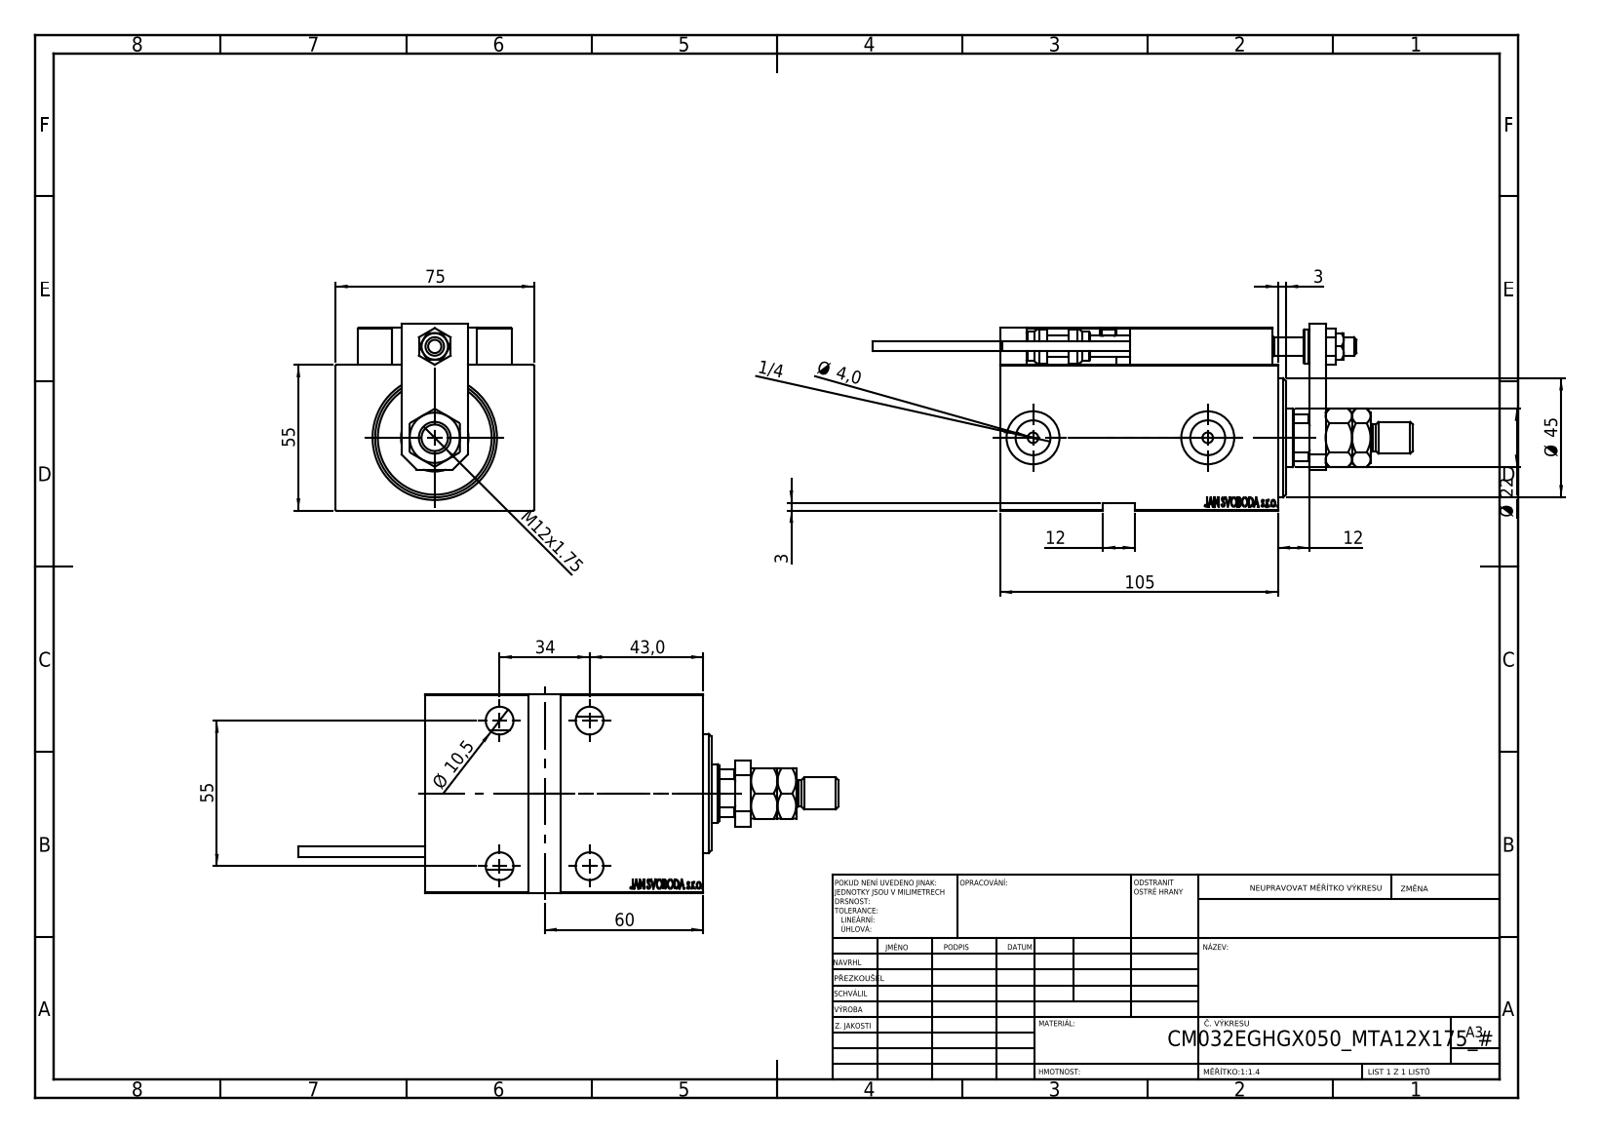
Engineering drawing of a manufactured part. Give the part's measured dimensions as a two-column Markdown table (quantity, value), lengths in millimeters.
| quantity | value |
| --- | --- |
| part name | SWITCH_X_FRONT_BACK; SWITCH X; SWITCH DIM B,W; ALLEN BOLT D5 (+7 more) |
| STEP written by | SolidWorks 2019 (CONFIG_CONTROL_DESIGN) |
| units | millimeters |
| bodies | 25 solids, 1339 faces (584 planar, 184 cylindrical, 571 other) |
| overall size | 204 × 75 × 70.5 |
| volume | 443 266 mm³ |
| surface area | 98 809 mm² |
| round holes (diameter × count) | 4 × 6, 8 × 5, 10.5 × 5, 16.5 × 5, 3.2 × 4, 5 × 2, 13.16 × 2, 20 × 2, 7 × 1, 22 × 1, 25.5 × 1, 32 × 1 |
| round bosses / shafts (diameter × count) | 5 × 2, 3.8 × 2, 34 × 1, 13 × 1, 12 × 1, 11 × 1, 10 × 1 |
| partial cylindrical surfaces (radius × count) | 0.3 × 30, 3 × 2, 10.5 × 1 |
| main face-to-face distances | 55, 75, 3, 10, 14, 69, 105, 12, 5, 95 |
| hole center spacings | 11.37, 20, 28.9, 29.59, 29.69, 34, 36.06, 40.03 |
